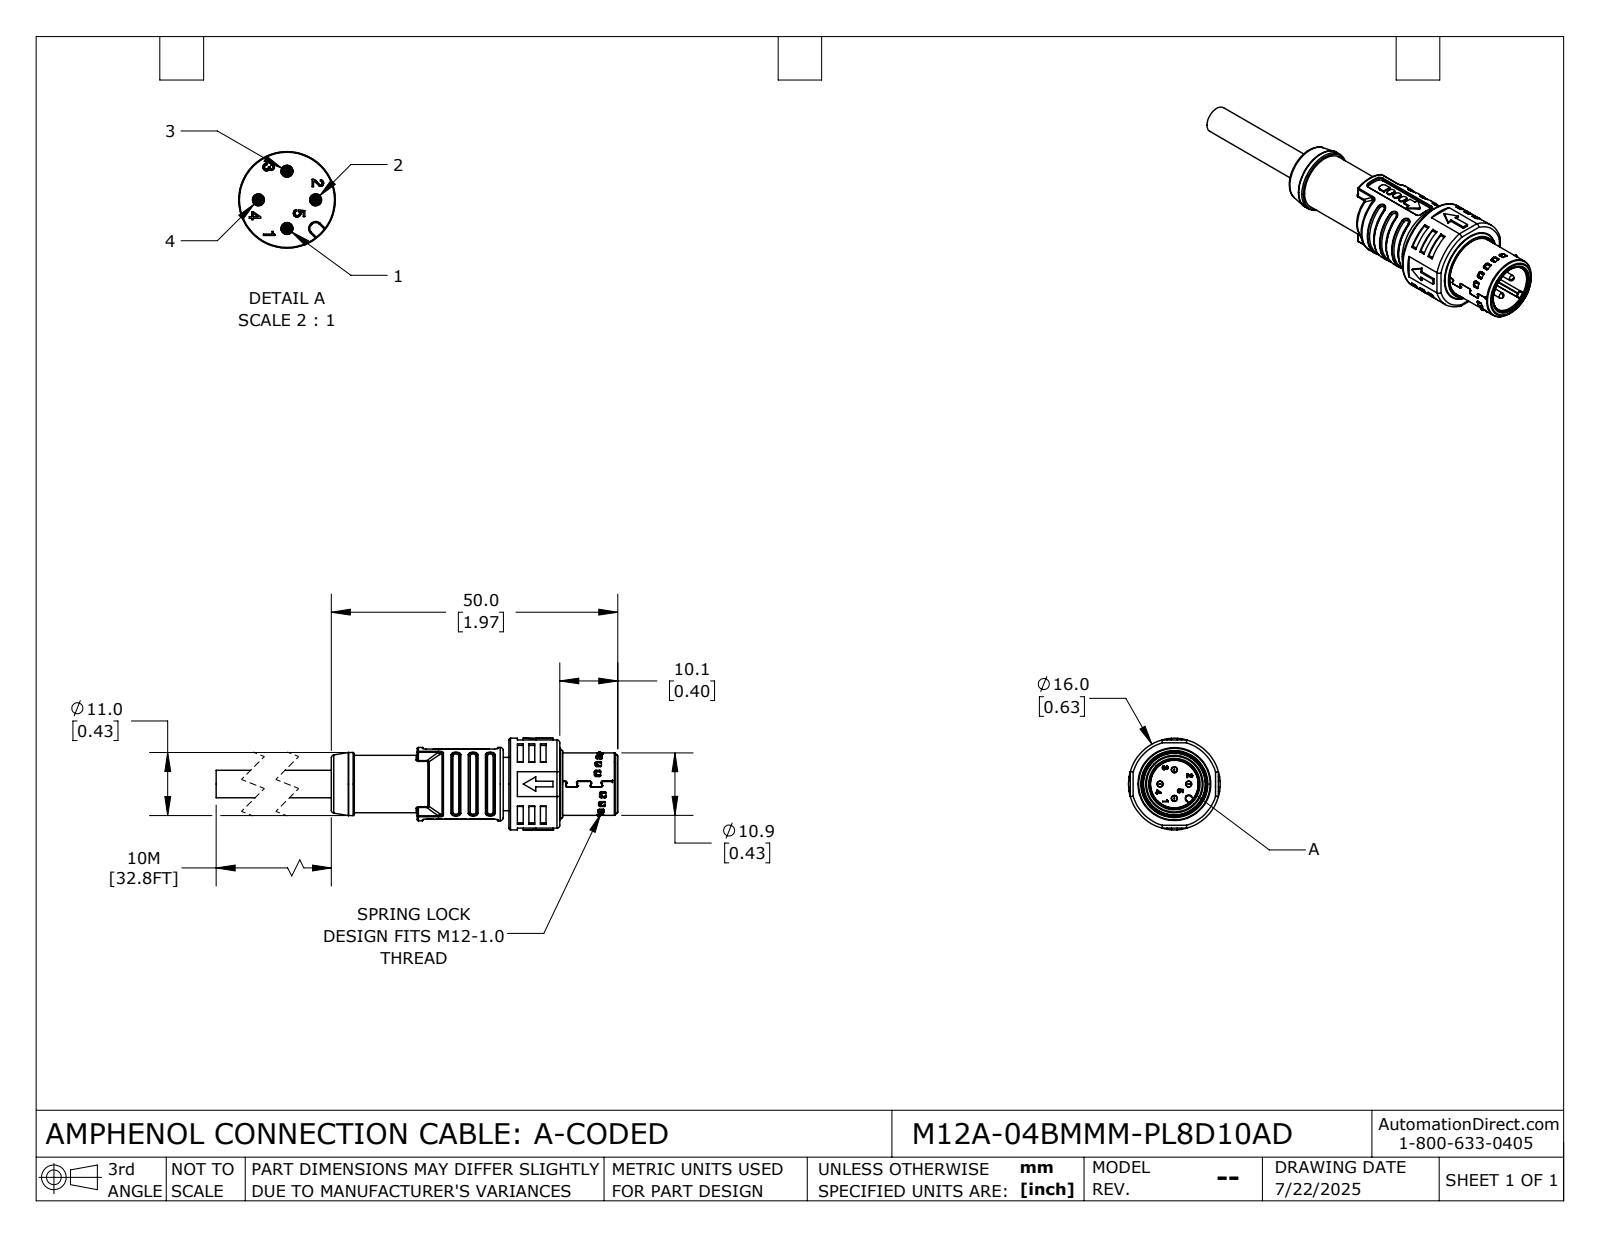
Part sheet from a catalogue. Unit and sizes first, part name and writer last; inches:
Units: inches
Overall size (bounding box): 2.862 × 0.63 × 0.63
Round holes (diameter × count): ⌀0.041 ×4, ⌀0.057 ×4, ⌀0.327 ×1, ⌀0.354 ×1, ⌀0.4 ×1, ⌀0.413 ×1, ⌀0.453 ×1, ⌀0.465 ×1, ⌀0.559 ×1
Round bosses / shafts (diameter × count): ⌀0.055 ×4, ⌀0.039 ×4, ⌀0.63 ×1, ⌀0.555 ×1, ⌀0.504 ×1, ⌀0.488 ×1, ⌀0.433 ×1, ⌀0.429 ×1
Partial cylindrical surfaces — rounded edges, fillets, slot ends (radius × count): R0.008 ×114, R0.01 ×66, R0.012 ×64, R0.006 ×44, R0.02 ×38, R0.005 ×12, R0.028 ×11, R0.004 ×10
Main face-to-face distances: 0.039, 0.398, 0.35, 0.339, 0.098, 0.059, 0.047, 1.28, 0.606, 1.618
Hole centre spacings: 0.098, 0.139, 0.197
Volume: 0.316 in³ · Surface area: 9.253 in²
Bodies: 1 solid, 2276 faces (1081 planar, 672 cylindrical, 523 other)
Part name (STEP PRODUCT): M12A-04BMMM-PL8D10AD
STEP written by: SolidWorks 2024 (CONFIG_CONTROL_DESIGN)
